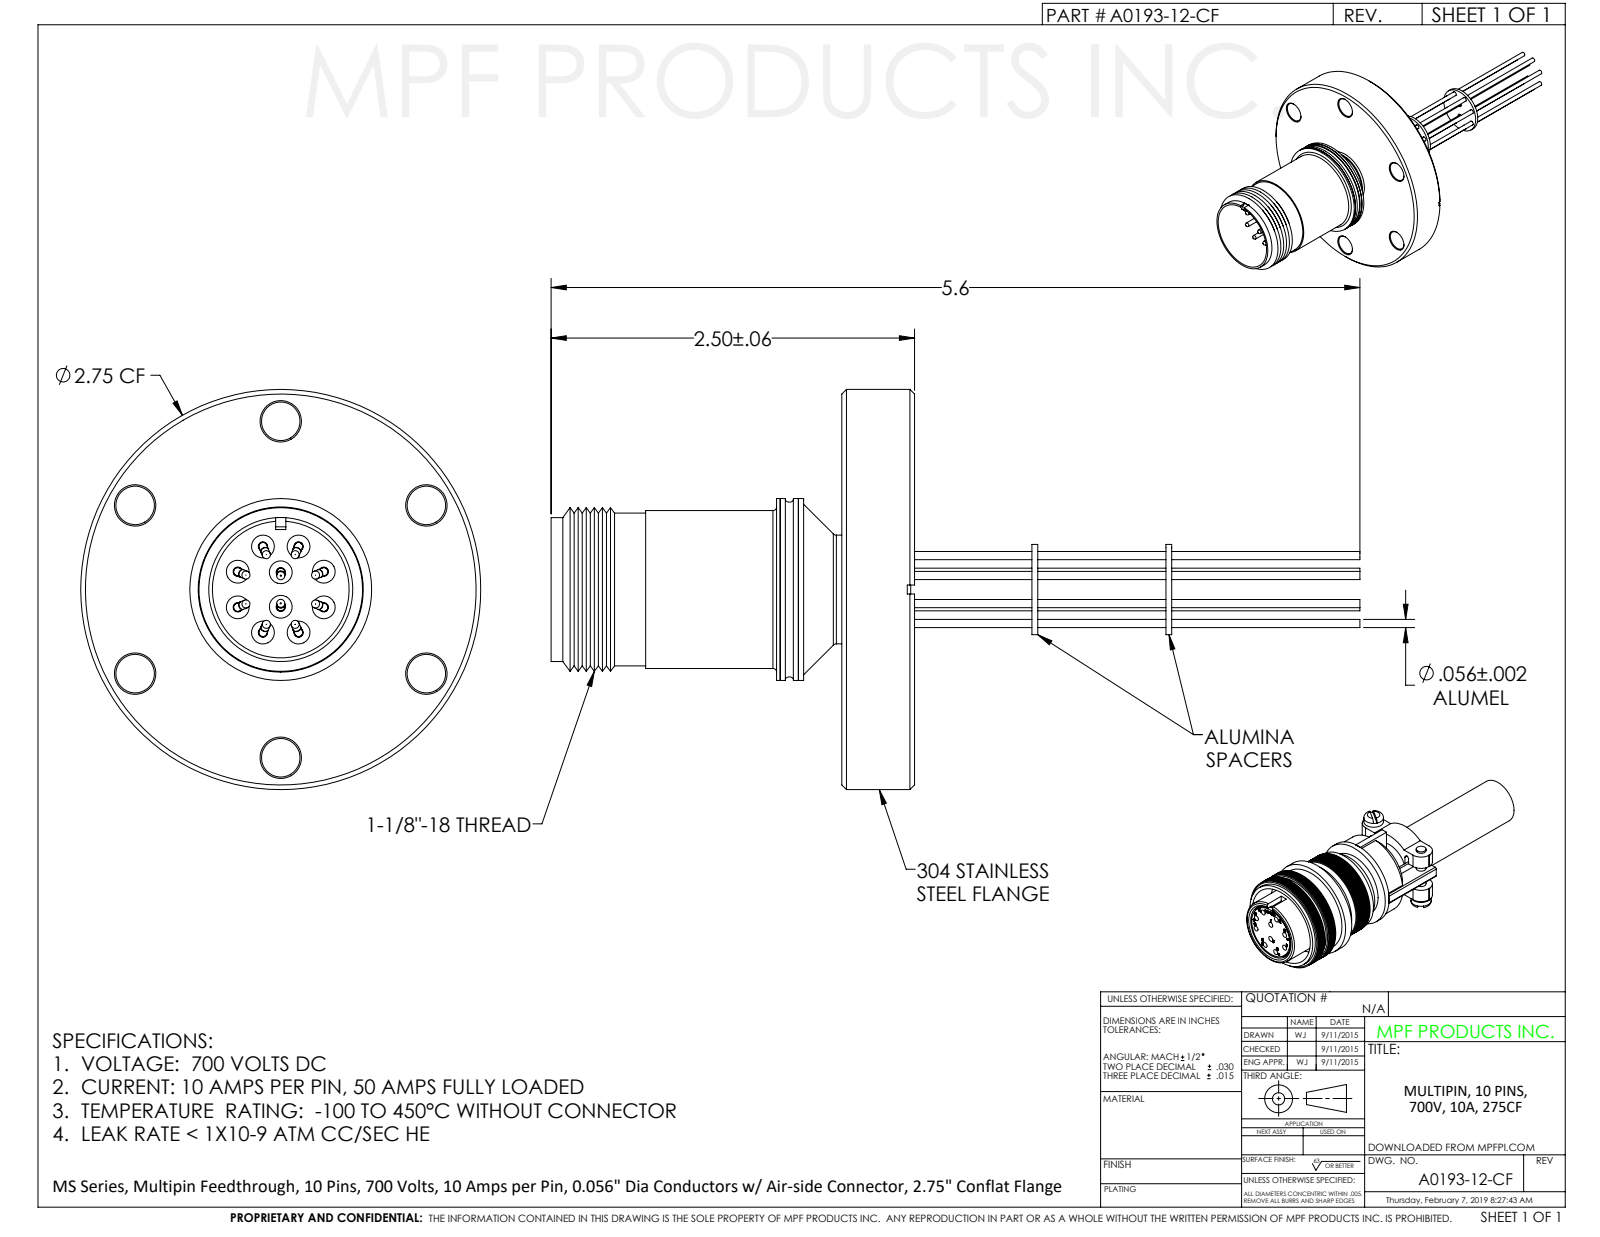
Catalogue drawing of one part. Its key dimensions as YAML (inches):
part_name: "A0193-12-CF"
step_written_by: "SolidWorks 2012 (CONFIG_CONTROL_DESIGN)"
units: inches
bodies: {solids: 1, faces: 427, planar: 86, cylindrical: 222, other: 119}
overall_size: [5.57, 2.75, 2.75]
volume: 3.221
surface_area: 50.23
round_holes:
  - {diameter: 0.265, count: 6}
  - {diameter: 0.675, count: 1}
  - {diameter: 0.94, count: 1}
  - {diameter: 0.96, count: 1}
  - {diameter: 0.97, count: 1}
  - {diameter: 1.035, count: 1}
  - {diameter: 1.65, count: 1}
  - {diameter: 1.902, count: 1}
round_bosses_or_shafts:
  - {diameter: 0.056, count: 30}
  - {diameter: 0.187, count: 10}
  - {diameter: 0.17, count: 10}
  - {diameter: 2.75, count: 1}
  - {diameter: 1.25, count: 1}
  - {diameter: 1.085, count: 1}
  - {diameter: 1.05, count: 1}
  - {diameter: 1.02, count: 1}
partial_cylinders:
  - {radius: 1.655, count: 2}
face_to_face_distances: [0.5, 0.449, 0.051, 0.04, 0.763, 0.856, 1.305, 1.356, 0.05, 0.806]
hole_center_spacings: [1.156, 2.002, 0.095, 1.074, 1.075, 1.159, 1.161, 1.239]
